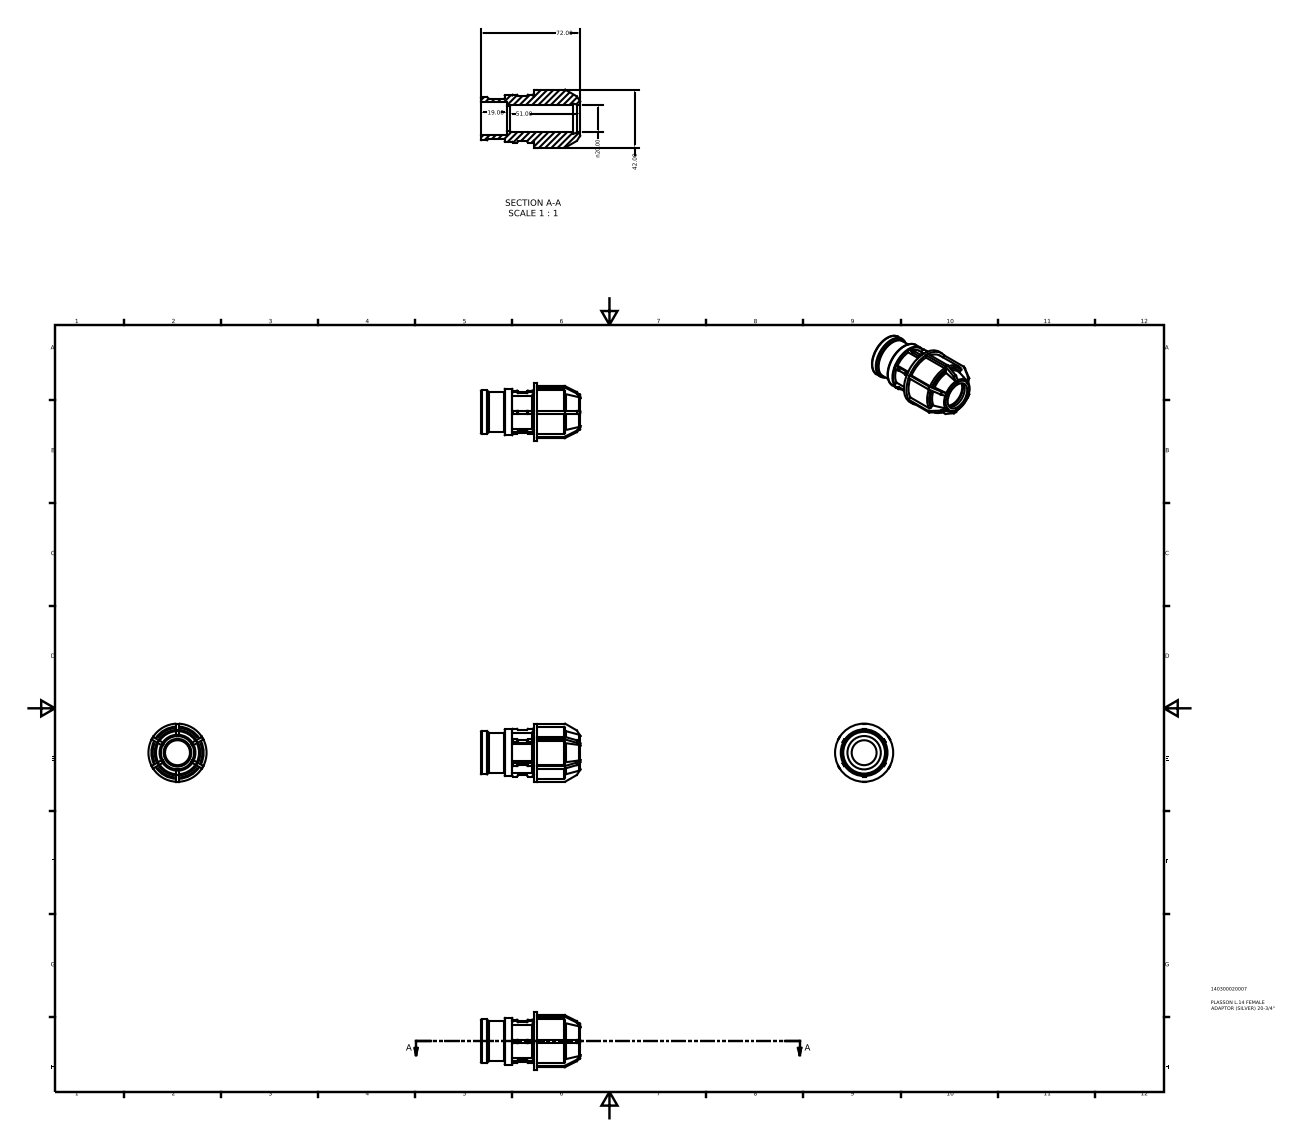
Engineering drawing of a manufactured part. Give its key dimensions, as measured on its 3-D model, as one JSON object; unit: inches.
{"part_name": "140300020007", "step_written_by": "Autodesk Inventor 2015 (AUTOMOTIVE_DESIGN)", "units": "inches", "bodies": {"solids": 1, "faces": 262, "planar": 160, "cylindrical": 68, "other": 34}, "overall_size": [2.835, 1.654, 1.654], "volume_in3": 2.226, "surface_area_in2": 24.65, "round_holes": [[0.709, 1], [0.787, 1], [0.95, 1]], "round_bosses_or_shafts": [[1.654, 1], [1.488, 1], [1.329, 1], [1.234, 1], [1.139, 1]], "partial_cylinders_radius": [[0.024, 48]], "face_to_face_distances": [0.083, 0.1, 1.509, 1.61, 0.152, 0.748, 0.761, 0.862, 0.073, 0.9]}
